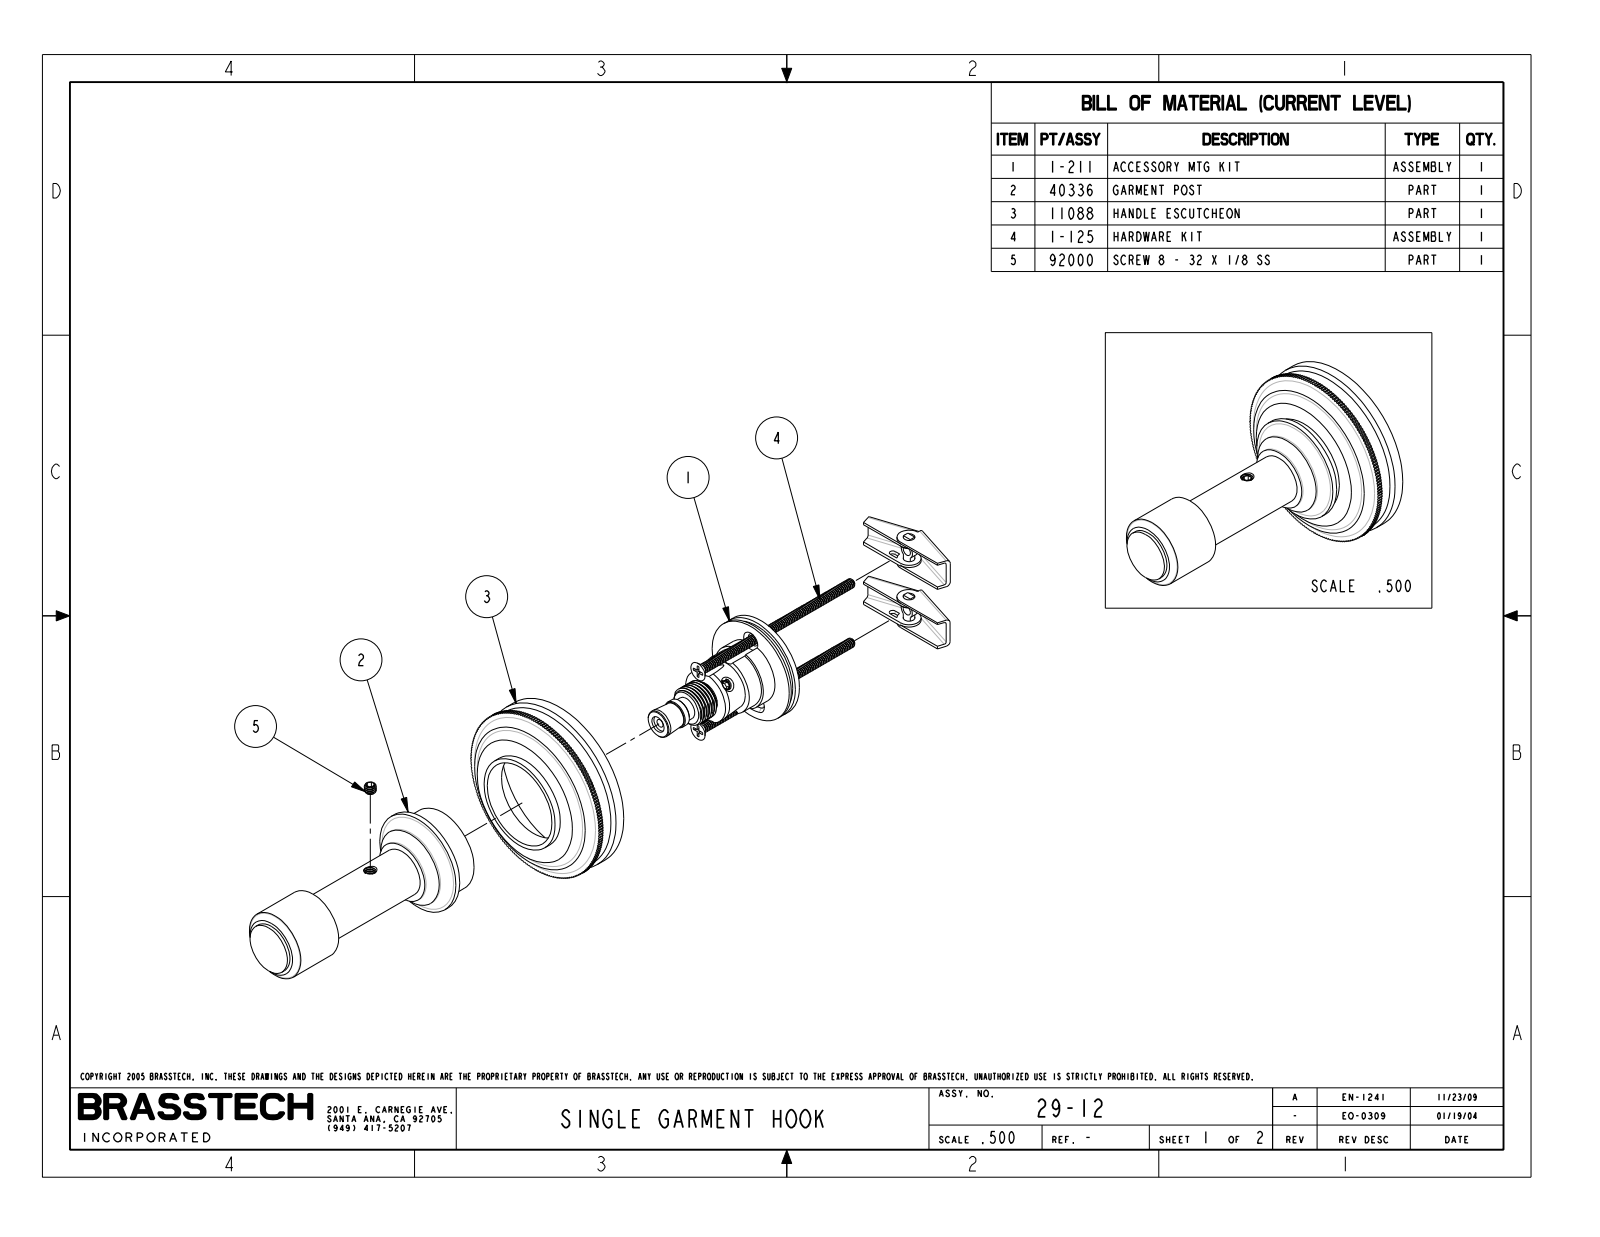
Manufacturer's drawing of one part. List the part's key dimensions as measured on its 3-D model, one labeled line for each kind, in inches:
Part name (STEP PRODUCT): 29-12_WEB
STEP written by: PRO/ENGINEER BY PARAMETRIC TECHNOLOGY CORPORATION, 2009300 (CONFIG_CONTROL_DESIGN)
Units: inches
Bodies: 0 solids, 584 faces (372 planar, 198 cylindrical, 14 other)
Overall size (bounding box): 3.75 × 2.5 × 2.5
Round bosses / shafts (diameter × count): ⌀2.5 ×1, ⌀2.4 ×1, ⌀1.48 ×1, ⌀1.38 ×1, ⌀1.134 ×1, ⌀1 ×1, ⌀0.88 ×1, ⌀0.725 ×1
Main face-to-face distances: 0.1, 0.475, 0.4, 0.075, 0.2, 0.575, 0.175, 0.675, 0.275, 0.075
